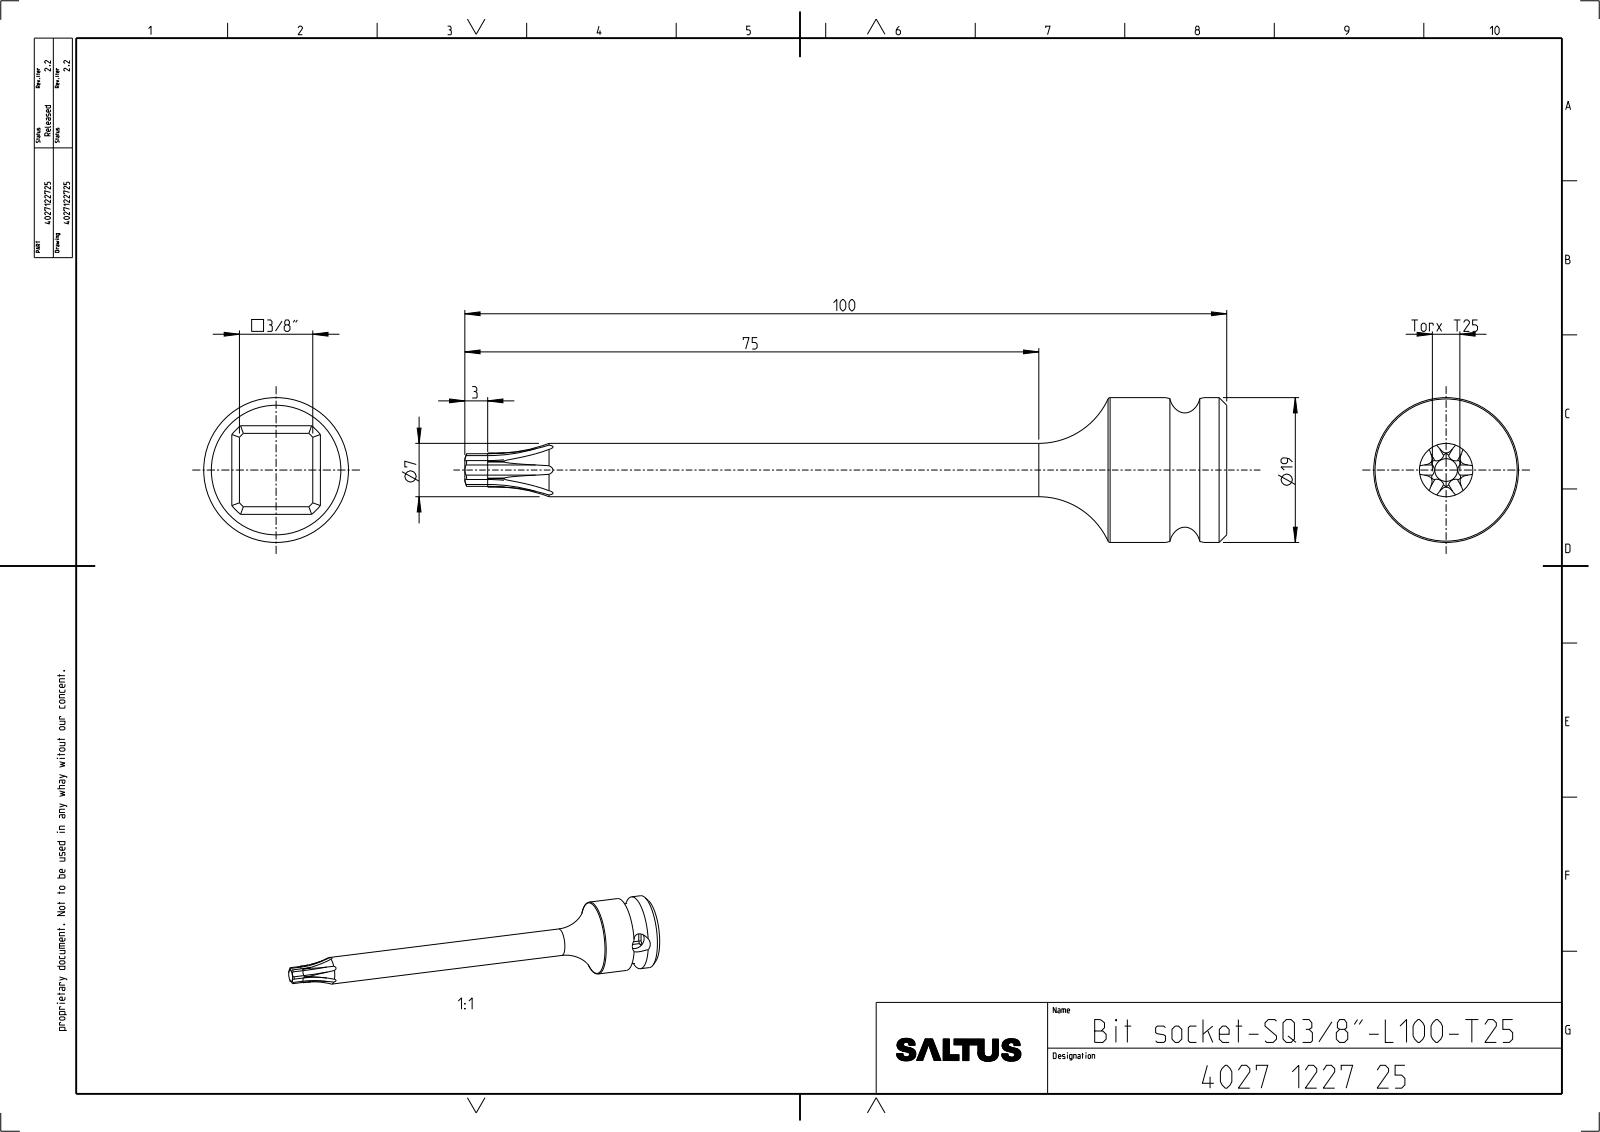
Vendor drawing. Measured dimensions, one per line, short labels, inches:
name: 4027122725
written by: CREO PARAMETRIC BY PTC INC, 2022414 (CONFIG_CONTROL_DESIGN)
unit: in
bodies: 1 solid, 93 faces (11 planar, 32 cylindrical, 50 other)
size: 3.937 × 0.748 × 0.748
volume: 0.39 in³; area: 5.702 in²
holes: 1× ⌀0.197
bosses: 1× ⌀0.748, 1× ⌀0.276
rounds: 6× R0.013, 6× R0.038, 1× R0.087, 1× R0.254
face distances: 0.379, 0.453, 3.937, 3.484
